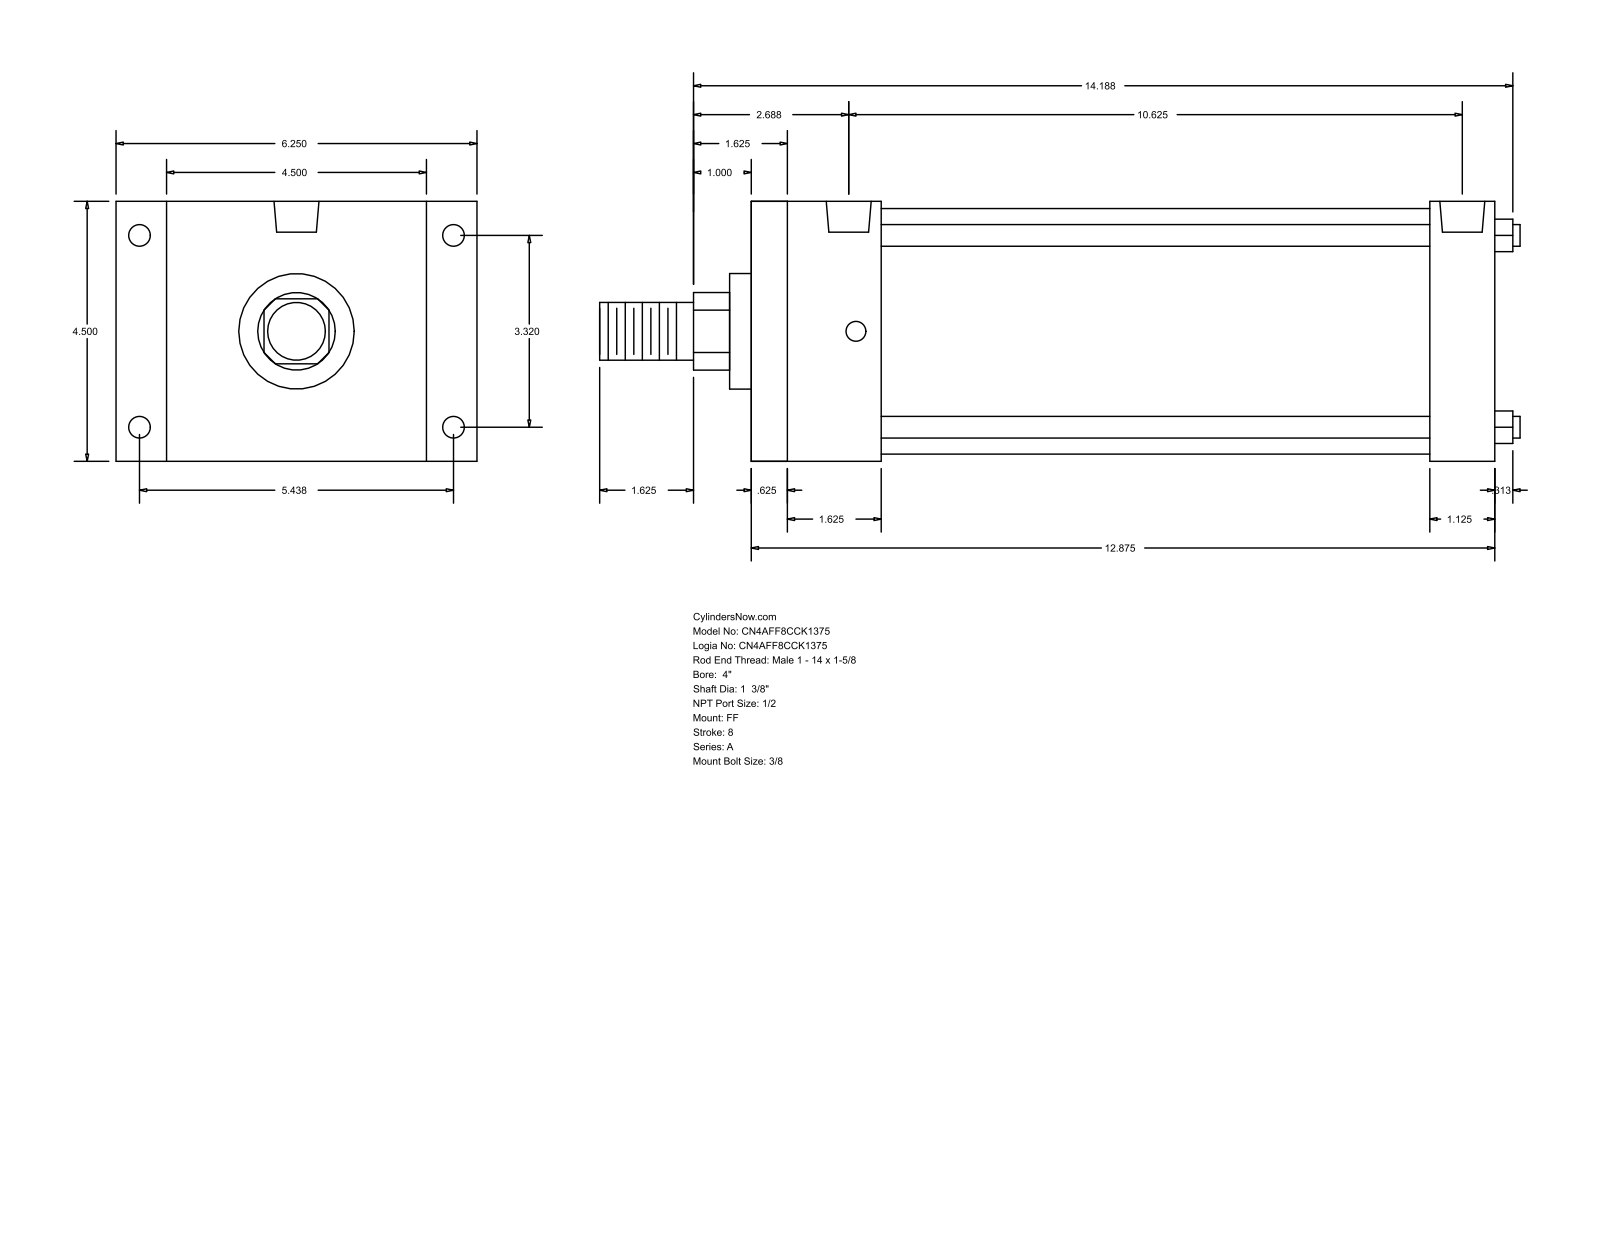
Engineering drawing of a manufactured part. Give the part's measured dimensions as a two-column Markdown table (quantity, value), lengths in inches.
| quantity | value |
| --- | --- |
| part name | A_FF__0400_1.375 |
| STEP written by | GSSL Pune (CONFIG_CONTROL_DESIGN) |
| units | inches |
| bodies | 0 solids, 92 faces (64 planar, 28 cylindrical, 0 other) |
| overall size | 15.937 × 6.25 × 4.5 |
| round holes (diameter × count) | 0.344 × 4, 0.375 × 4, 0.778 × 2 |
| round bosses / shafts (diameter × count) | 0.375 × 4, 4.25 × 1, 2 × 1, 1.375 × 1, 1 × 1 |
| partial cylindrical surfaces (radius × count) | 0.672 × 1 |
| main face-to-face distances | 4.5, 12.875, 0.625, 12.25, 2.25, 1.125, 0.875, 5.375, 11.75, 11.125 |
| hole center spacings | 0.125, 3.32, 5.438, 6.371, 10.375, 10.5, 10.625 |
